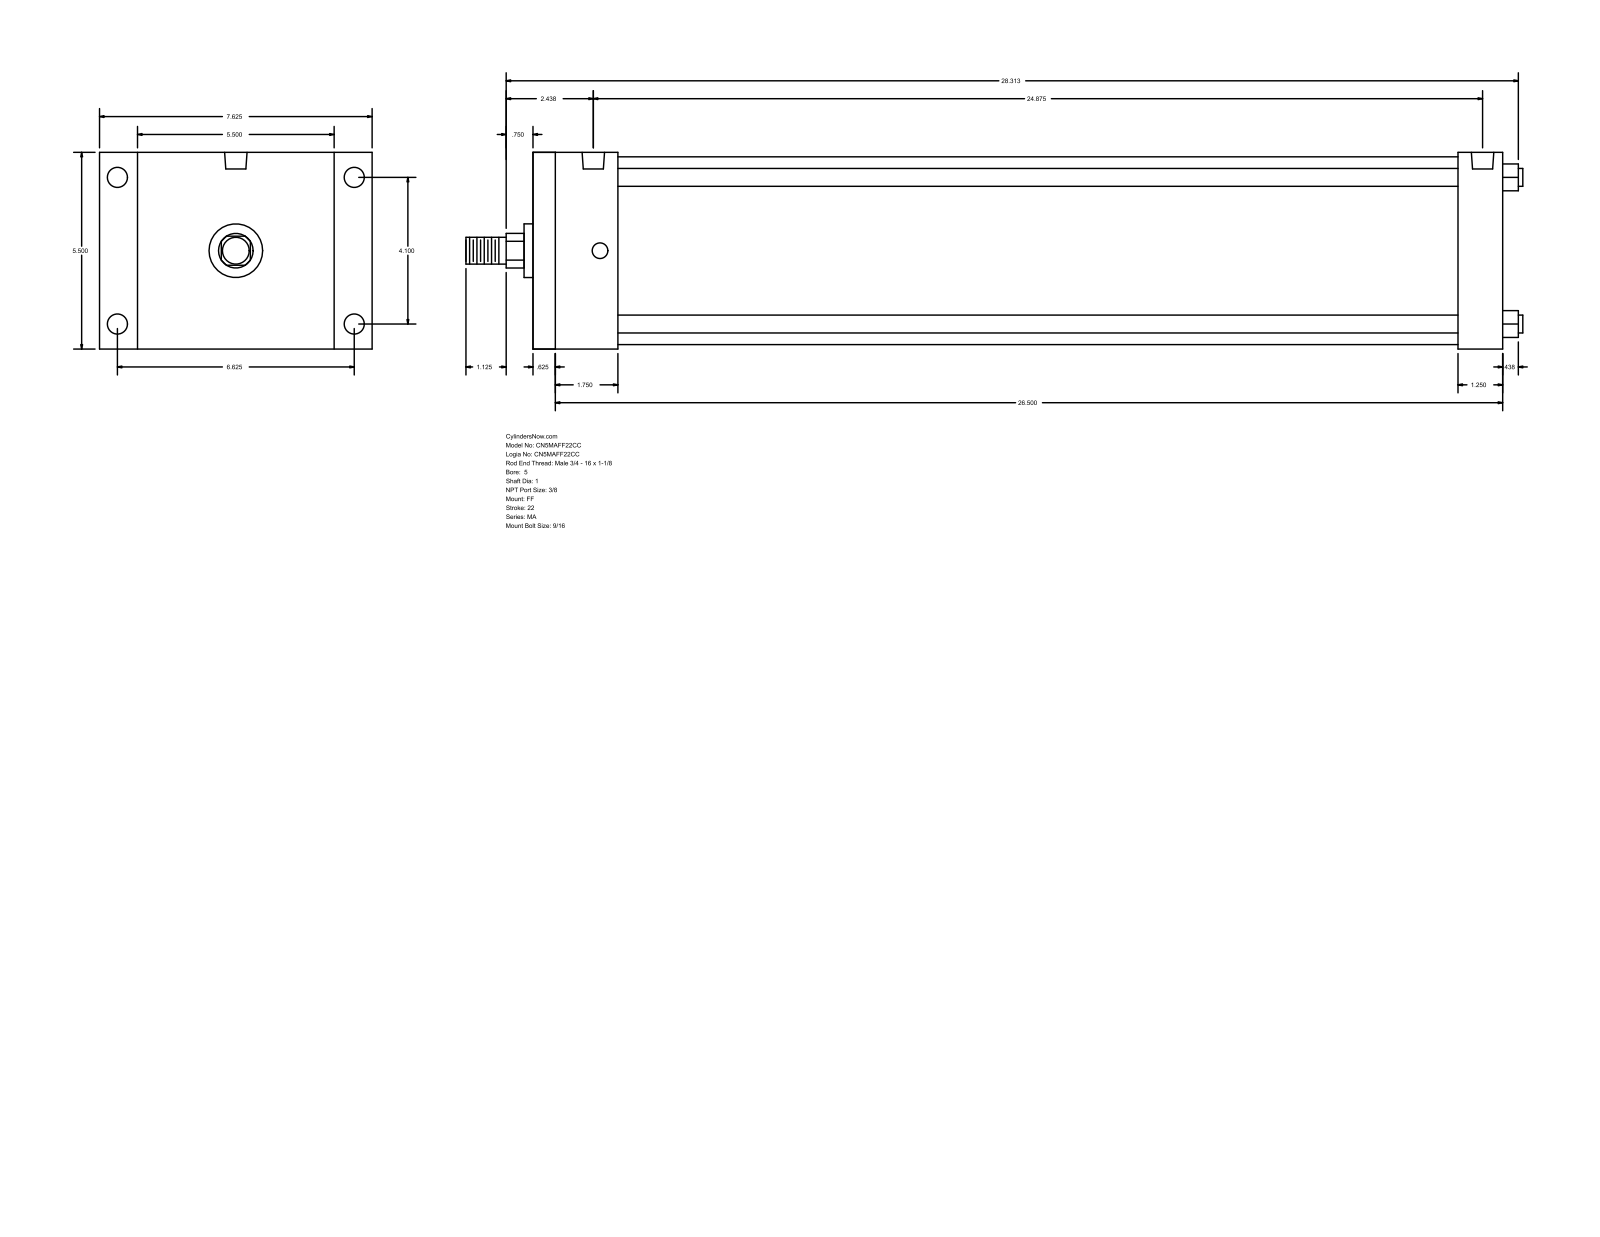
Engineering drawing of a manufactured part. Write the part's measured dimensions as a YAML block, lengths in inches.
part_name: "MA_FF__0500_1"
step_written_by: "GSSL Pune (CONFIG_CONTROL_DESIGN)"
units: inches
bodies: {solids: 0, faces: 92, planar: 64, cylindrical: 28, other: 0}
overall_size: [29.563, 7.625, 5.5]
round_holes:
  - {diameter: 0.437, count: 4}
  - {diameter: 0.563, count: 4}
  - {diameter: 0.627, count: 2}
round_bosses_or_shafts:
  - {diameter: 0.5, count: 4}
  - {diameter: 5.25, count: 1}
  - {diameter: 1.5, count: 1}
  - {diameter: 1, count: 1}
  - {diameter: 0.75, count: 1}
partial_cylinders:
  - {radius: 0.484, count: 1}
face_to_face_distances: [5.5, 27.125, 0.625, 26.5, 25.875, 25.25, 1.25, 2.375, 1.75, 23.5]
hole_center_spacings: [0.187, 4.1, 6.625, 7.791, 24.5, 24.688, 24.875]
